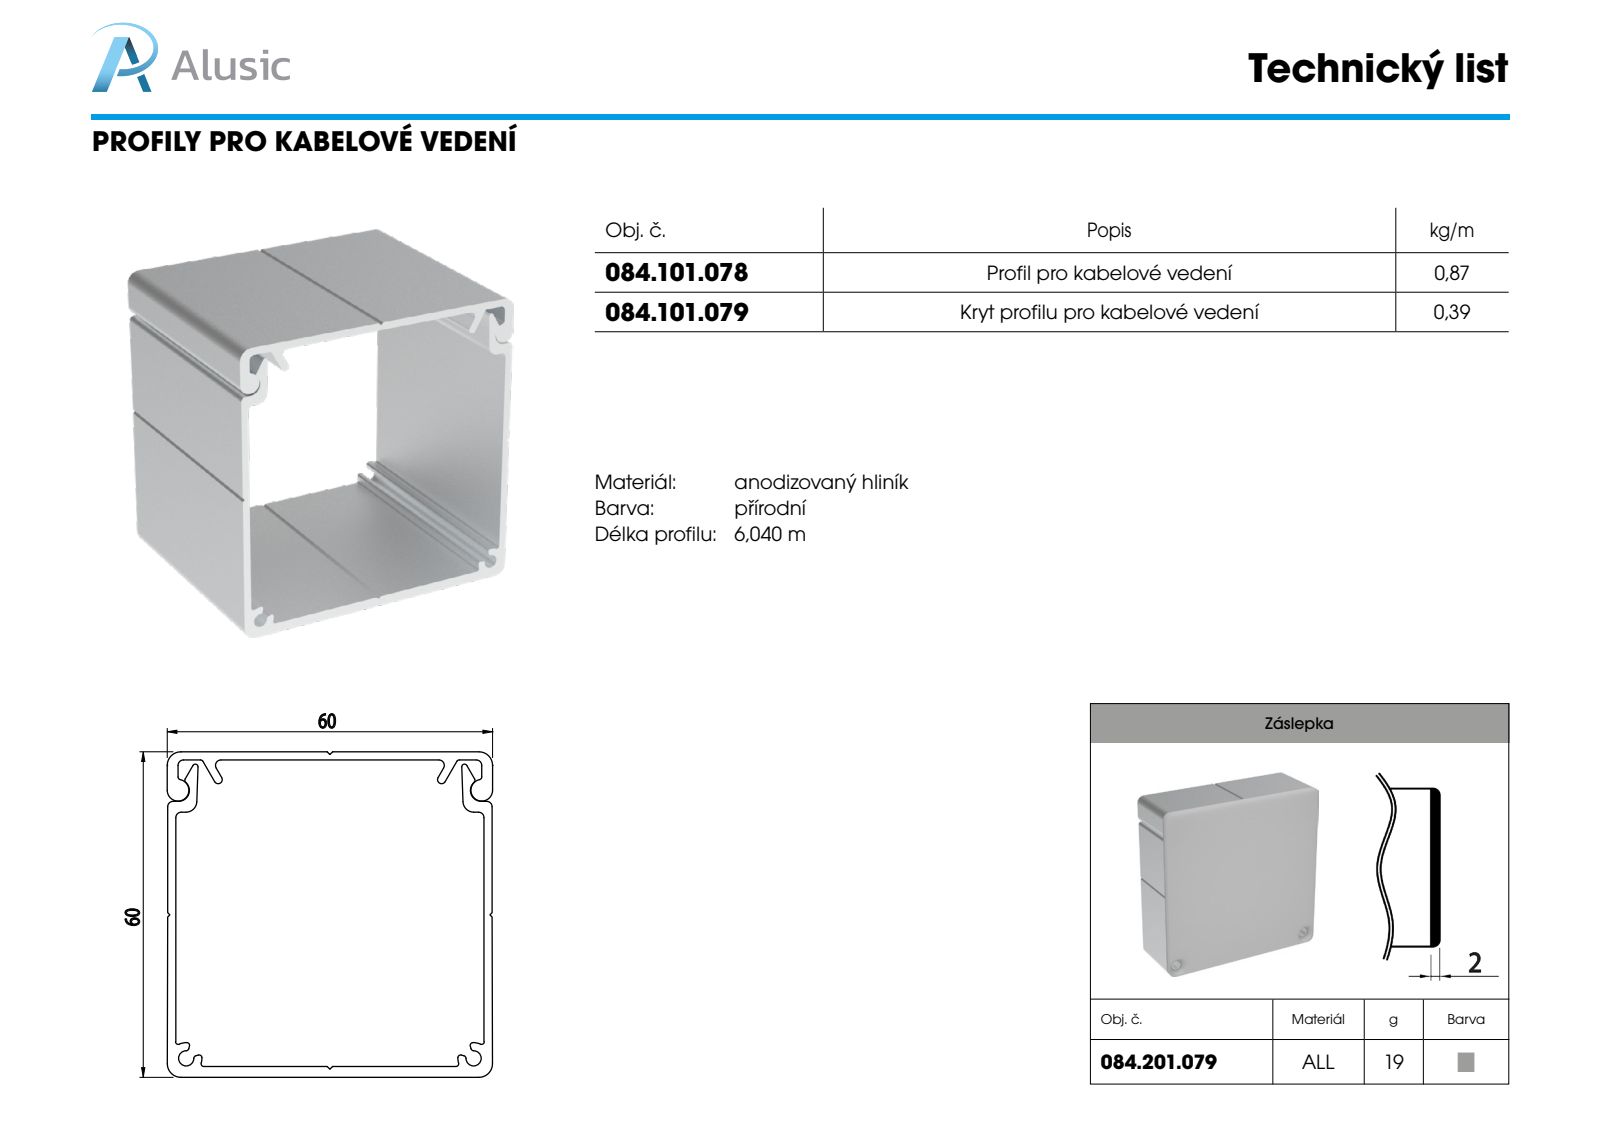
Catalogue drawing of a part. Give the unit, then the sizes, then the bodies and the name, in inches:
Units: inches
Overall size (bounding box): 3.937 × 2.362 × 0.357
Partial cylindrical surfaces — rounded edges, fillets, slot ends (radius × count): R0.02 ×4, R0.039 ×4, R0.004 ×3, R0.03 ×2, R0.079 ×2, R0.098 ×2
Main face-to-face distances: 0.059, 2.362, 0.079, 2.283, 2.205, 3.937
Volume: 0.882 in³ · Surface area: 26.54 in²
Bodies: 1 solid, 34 faces (17 planar, 17 cylindrical, 0 other)
Part name (STEP PRODUCT): 084.101.079
STEP written by: SolidWorks 2018 (AUTOMOTIVE_DESIGN)
